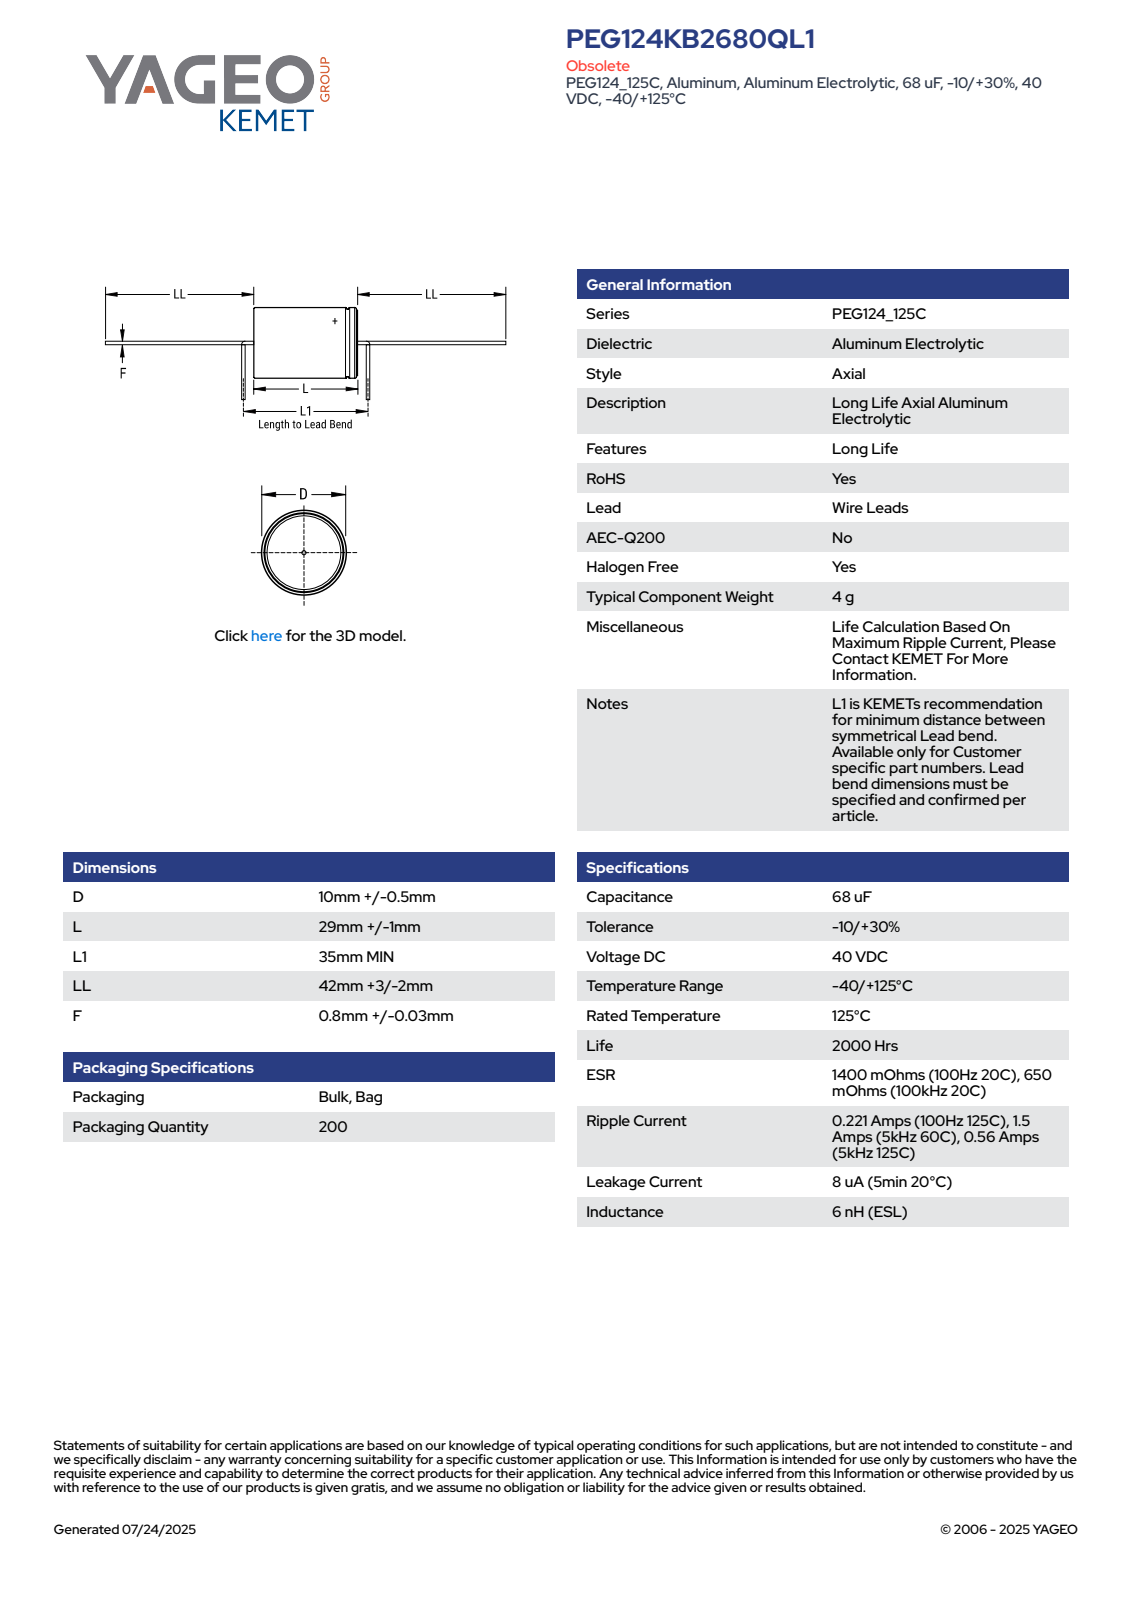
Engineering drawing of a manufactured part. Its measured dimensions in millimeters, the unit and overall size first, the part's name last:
Units: millimetres
Overall size (bounding box): 117 × 10.5 × 10.5
Round holes (diameter × count): ⌀9.5 ×1
Round bosses / shafts (diameter × count): ⌀10.5 ×1, ⌀10 ×1, ⌀0.83 ×1
Partial cylindrical surfaces — rounded edges, fillets, slot ends (radius × count): R5.24 ×1
Main face-to-face distances: 29, 30, 1, 45, 74, 75, 117, 72, 43, 42
Volume: 2 569 mm³ · Surface area: 1 424 mm²
Bodies: 1 solid, 99 faces (27 planar, 29 cylindrical, 43 other)
Part name (STEP PRODUCT): CAA_PEG124_10X29_D10.5L30LL45F0.83
STEP written by: SolidWorks 2014 (AUTOMOTIVE_DESIGN)
